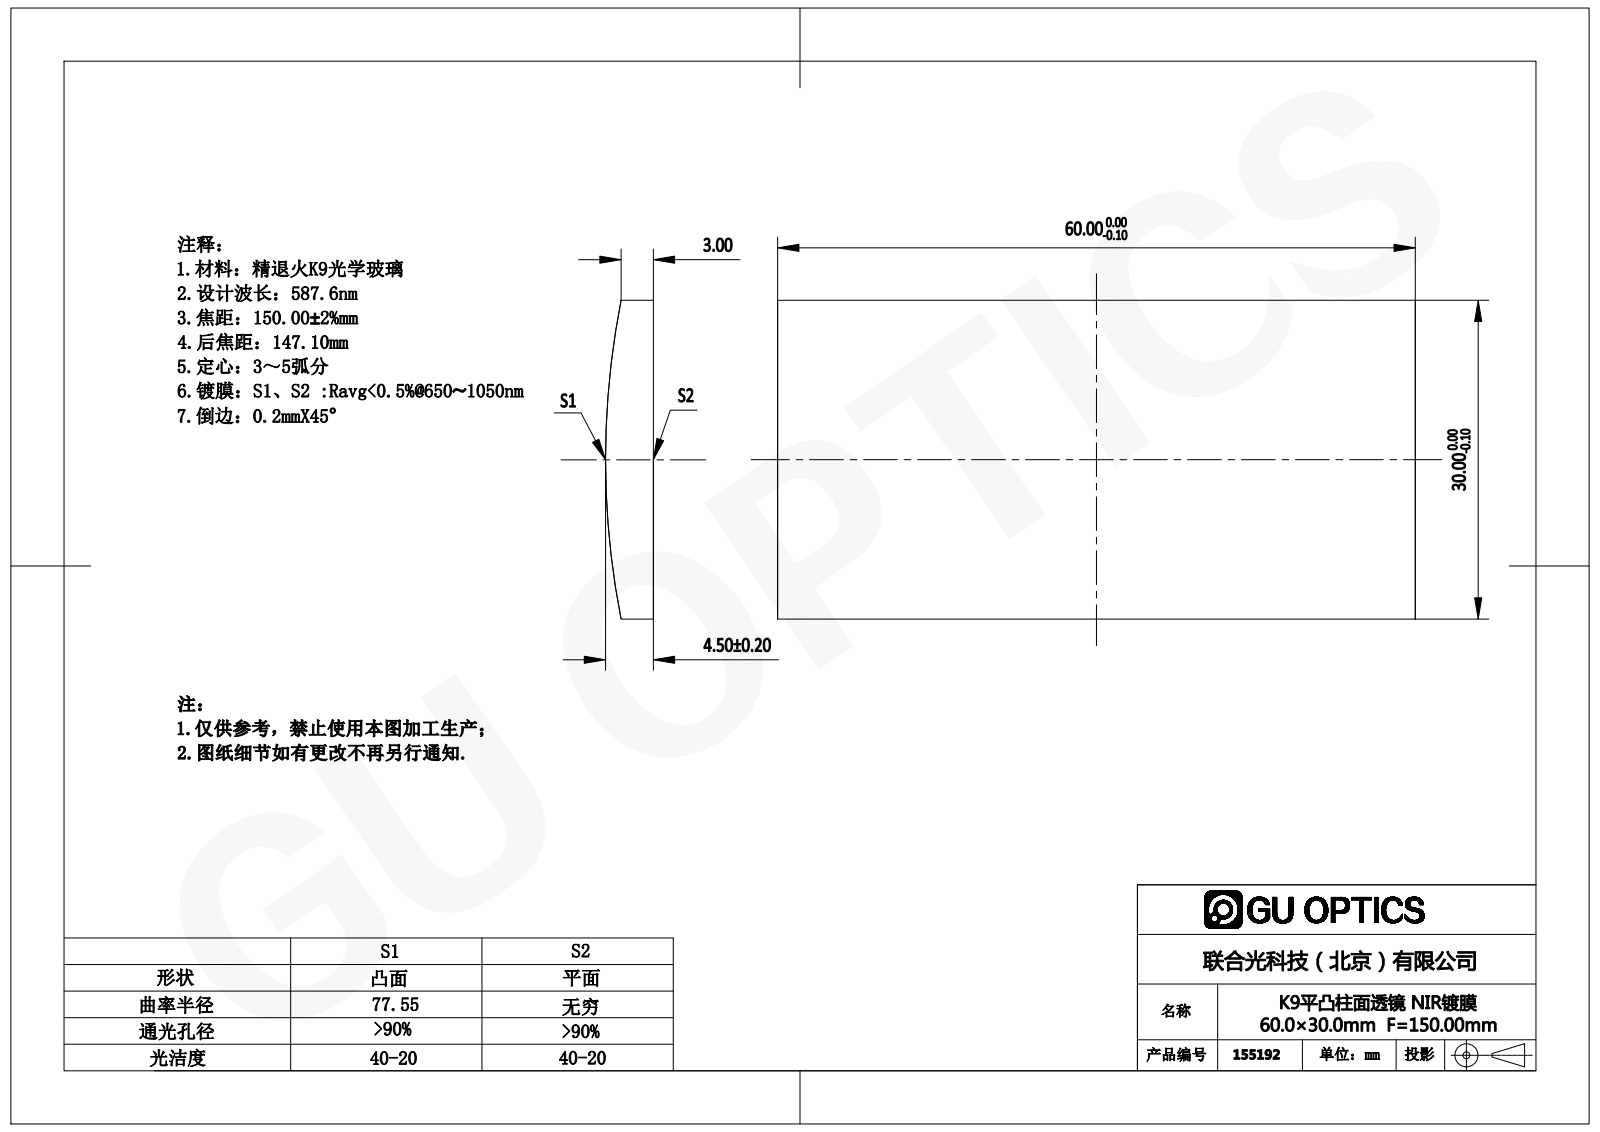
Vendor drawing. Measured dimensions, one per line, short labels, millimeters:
name: 155060
written by: SolidWorks 2016 (AUTOMOTIVE_DESIGN)
unit: mm
bodies: 1 solid, 6 faces (5 planar, 1 cylindrical, 0 other)
size: 60 × 30 × 4.5
volume: 7 225 mm³; area: 4 216 mm²
rounds: 1× R77.55
face distances: 30, 60
